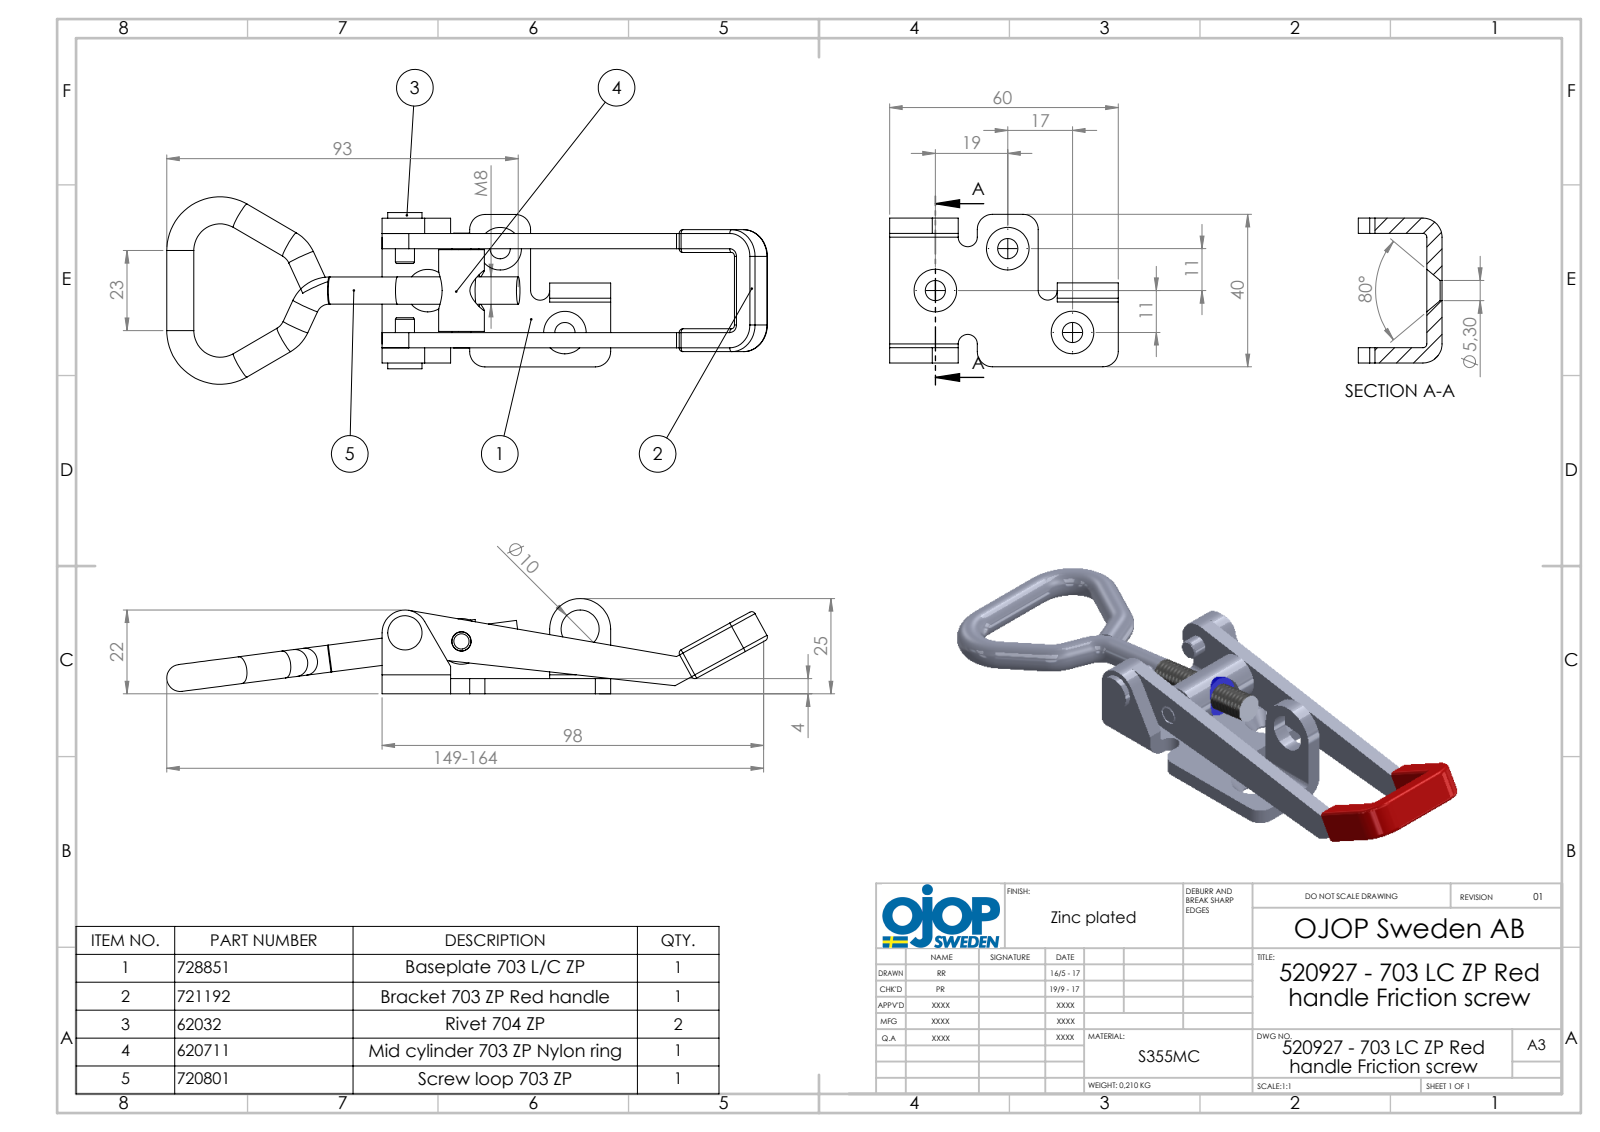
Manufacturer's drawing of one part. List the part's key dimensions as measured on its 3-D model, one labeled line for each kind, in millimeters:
Part name (STEP PRODUCT): 704 - Rivet Gradin; 704 - Friction ring; 703 - Skruvögla; 703- Platta LC (+4 more)
STEP written by: SolidWorks 2015 (AUTOMOTIVE_DESIGN)
Units: millimetres
Bodies: 7 solids, 220 faces (69 planar, 99 cylindrical, 52 other)
Overall size (bounding box): 161.12 × 49.4 × 25
Volume: 28 207 mm³ · Surface area: 19 074 mm²
Round holes (diameter × count): ⌀5.3 ×3, ⌀5.1 ×2, ⌀6.9 ×1, ⌀7.2 ×1, ⌀7.7 ×1, ⌀10 ×1, ⌀10.5 ×1
Round bosses / shafts (diameter × count): ⌀7 ×4, ⌀5 ×2, ⌀12 ×1, ⌀10.5 ×1, ⌀9 ×1, ⌀7.7 ×1
Partial cylindrical surfaces — rounded edges, fillets, slot ends (radius × count): R1 ×23, R4 ×4, R2.5 ×3, R5 ×3, R7 ×2, R6 ×1, R8 ×1
Main face-to-face distances: 4, 26, 30, 22, 17, 13, 9, 21, 8, 5
Hole centre spacings: 15.01, 21.95, 27.8, 31.33, 37.64, 46.01
